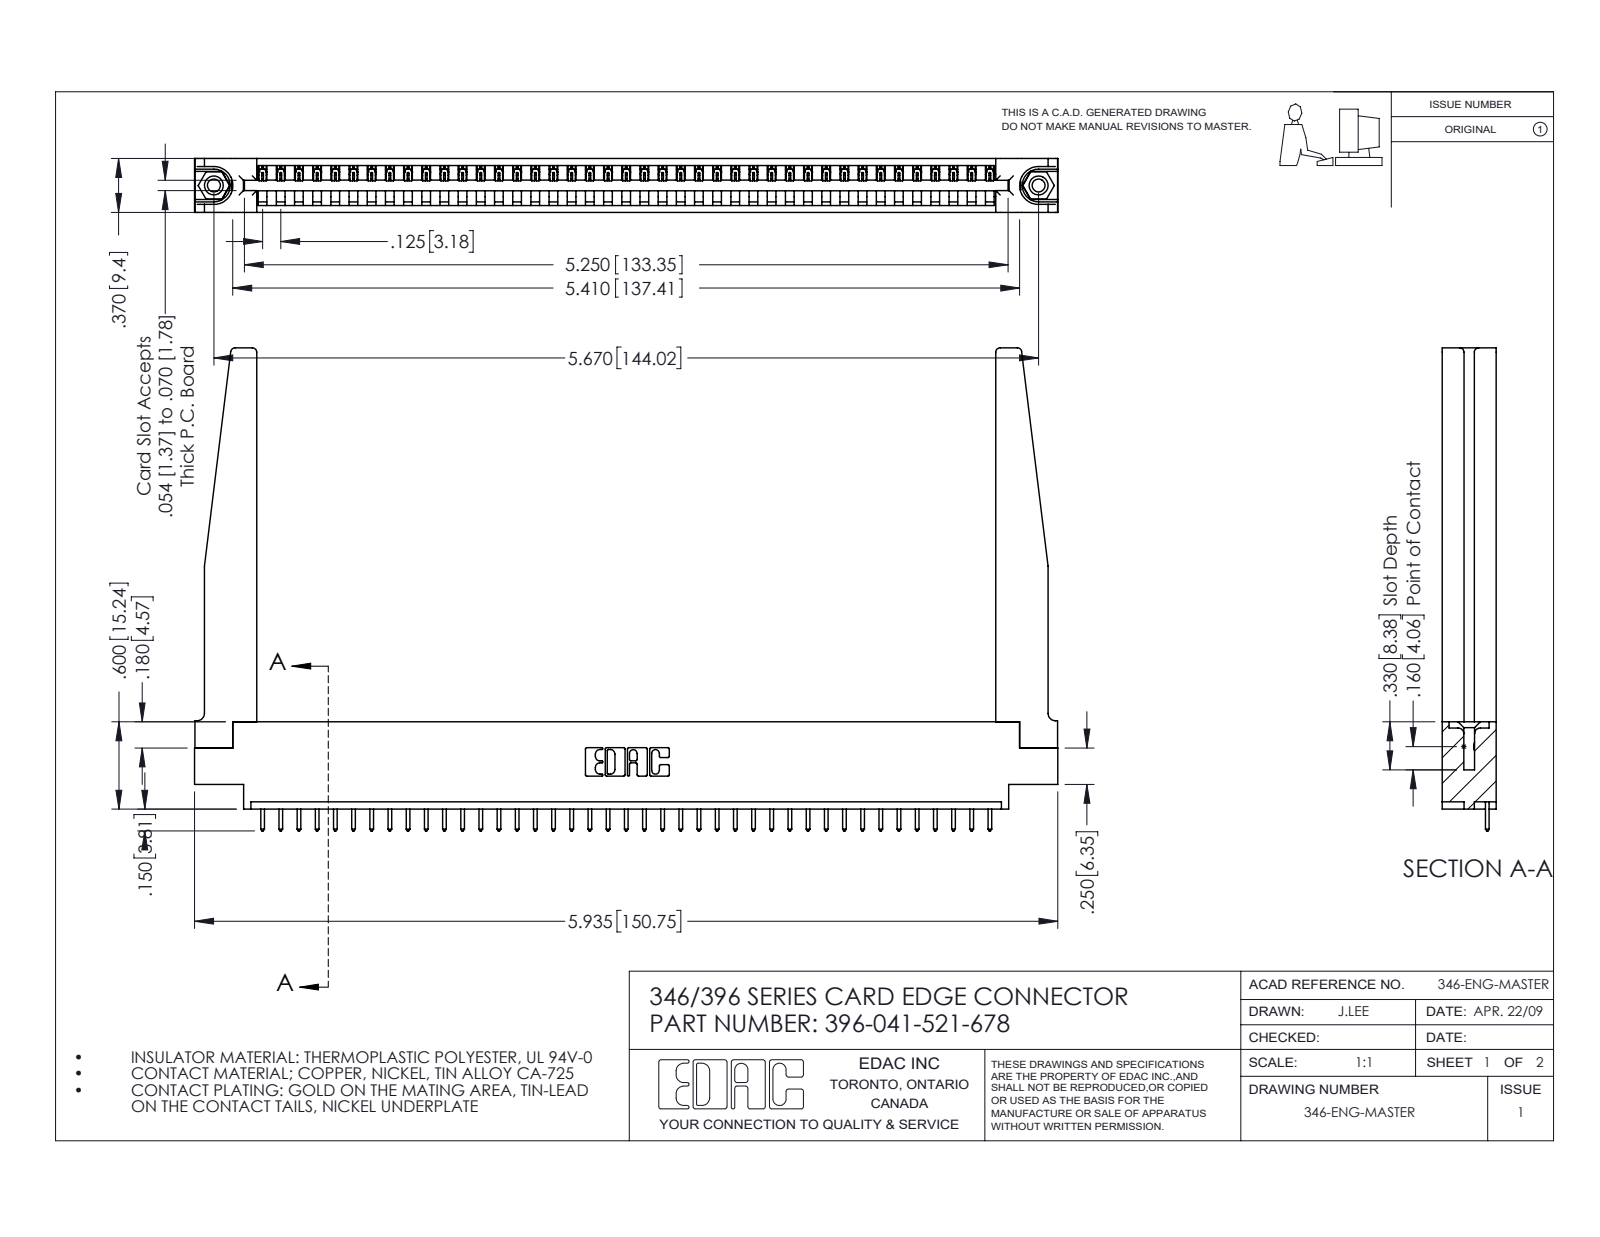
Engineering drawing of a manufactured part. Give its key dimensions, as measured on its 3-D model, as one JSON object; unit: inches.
{"part_name": "346-220-078_345-220-078; 345-292-001_345-293-121; 396-041-521-678; 345-250-001_345-250-001-102 (+1 more)", "step_written_by": "SolidWorks 2016 (CONFIG_CONTROL_DESIGN)", "units": "inches", "bodies": {"solids": 46, "faces": 2738, "planar": 1862, "cylindrical": 824, "other": 52}, "overall_size": [5.935, 3.32, 0.37], "volume_in3": 1.285, "surface_area_in2": 37.07, "round_holes": [[0.089, 2], [0.125, 2], [0.156, 2], [0.064, 1]], "round_bosses_or_shafts": [[0.155, 2]], "partial_cylinders_radius": [[0.006, 82], [0.01, 82], [0.01, 22], [0.03, 8], [0.007, 6], [0.031, 6], [0.026, 3], [0.031, 2]], "face_to_face_distances": [0.37, 0.048, 0.322, 0.072, 0.148, 0.15, 0.25, 0.298, 0.025, 0.222], "hole_center_spacings": [0.246, 5.461, 5.67]}
